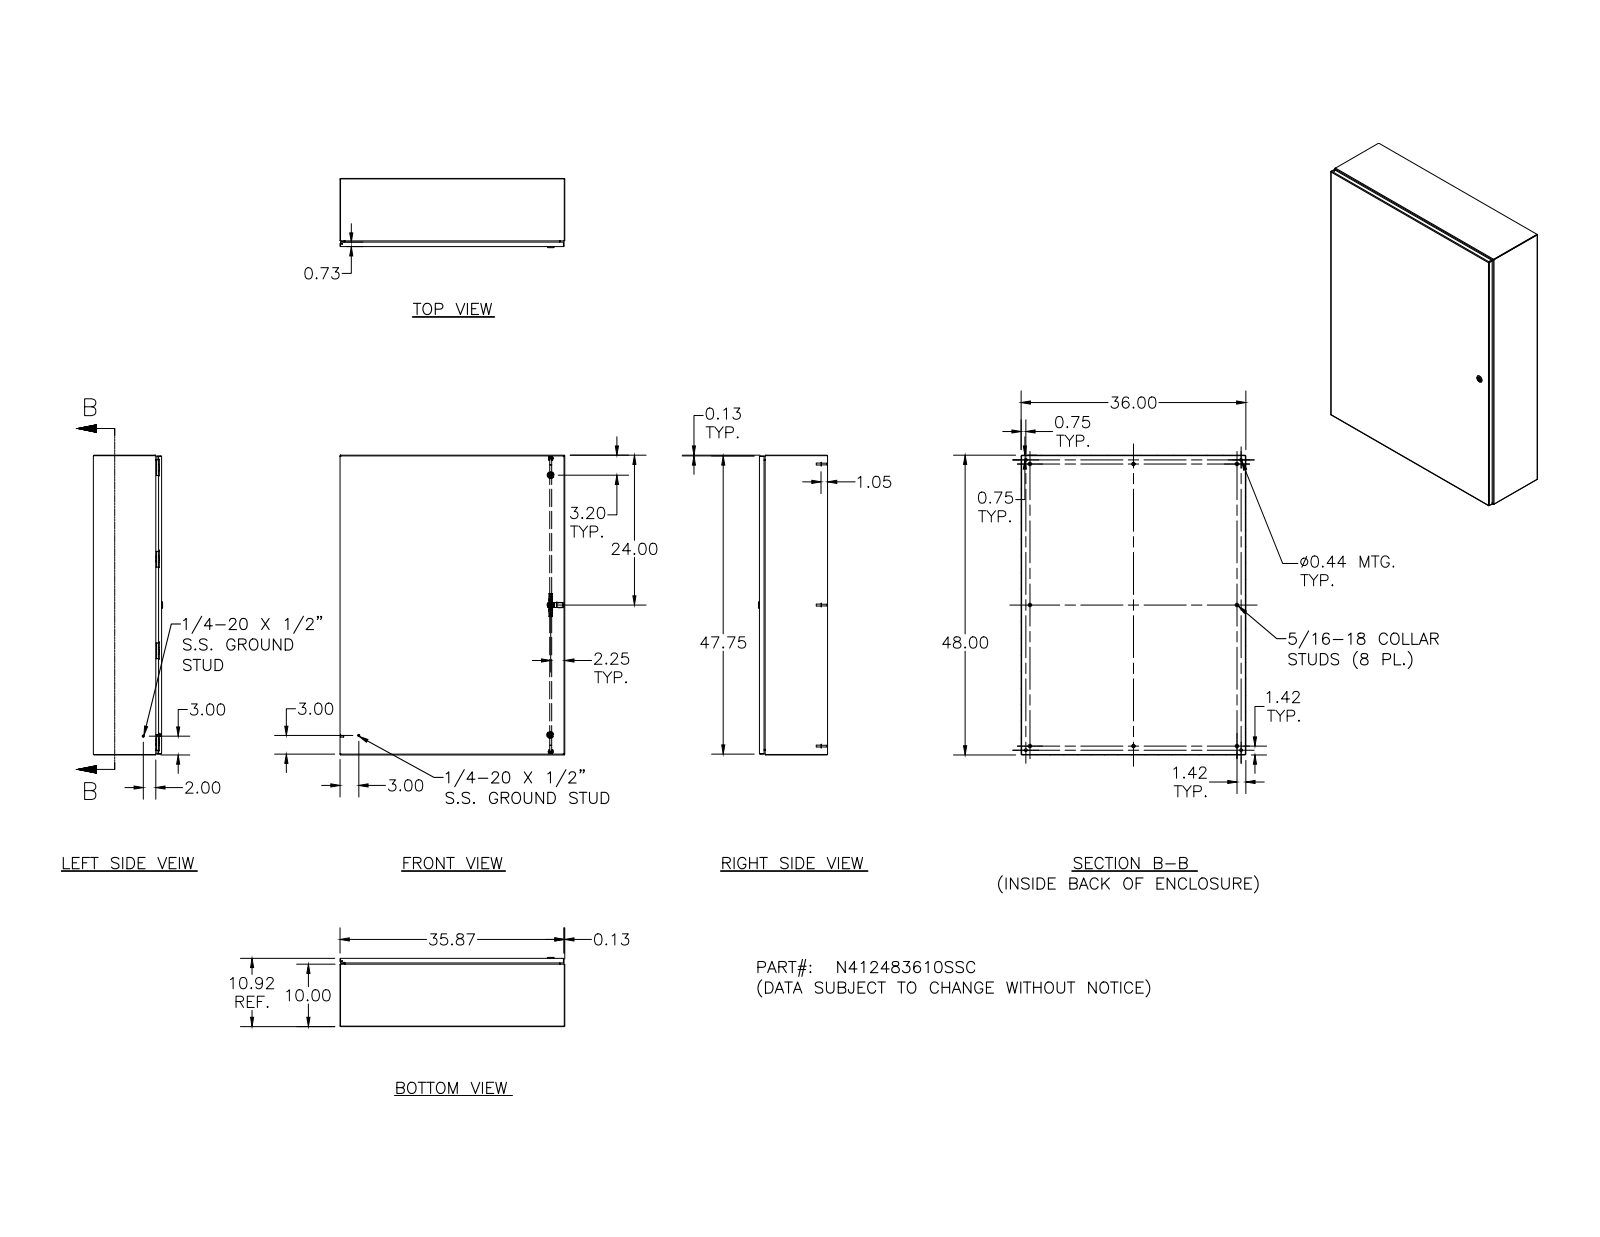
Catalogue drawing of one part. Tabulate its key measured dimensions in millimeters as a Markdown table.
| quantity | value |
| --- | --- |
| part name | N412483610SSC; N412483610SSCBLR; N4123610SSCTB; 388151 (+8 more) |
| STEP written by | Autodesk Inventor 2011 (AUTOMOTIVE_DESIGN) |
| units | millimeters |
| bodies | 81 solids, 2661 faces (988 planar, 992 cylindrical, 681 other) |
| overall size | 1219.2 × 914.4 × 281.3 |
| volume | 6 725 000 mm³ |
| surface area | 7 143 000 mm² |
| round holes (diameter × count) | 2.4 × 8, 3.9 × 8, 4.2 × 8, 4.4 × 8, 4.7 × 8, 5 × 5, 4 × 4, 4.2 × 4, 11.1 × 4, 2.7 × 2, 4.1 × 2, 4.3 × 2 |
| round bosses / shafts (diameter × count) | 6.4 × 18, 14.3 × 8, 9.1 × 8, 8.1 × 8, 7.6 × 8, 7 × 8, 6.5 × 8, 4.2 × 8 |
| partial cylindrical surfaces (radius × count) | 1.3 × 50, 0.8 × 36, 0.4 × 34, 3.2 × 32, 0.3 × 30, 0.5 × 20, 2.7 × 18, 3 × 18 |
| main face-to-face distances | 1.9, 275.4, 273.5, 277.3, 912.5, 1217.3, 910.6, 914.4, 1215.4, 1219.2 |
| hole center spacings | 372.5, 745.1, 372.5, 1117.6, 12.7, 16.7, 33.2, 372.7 |
